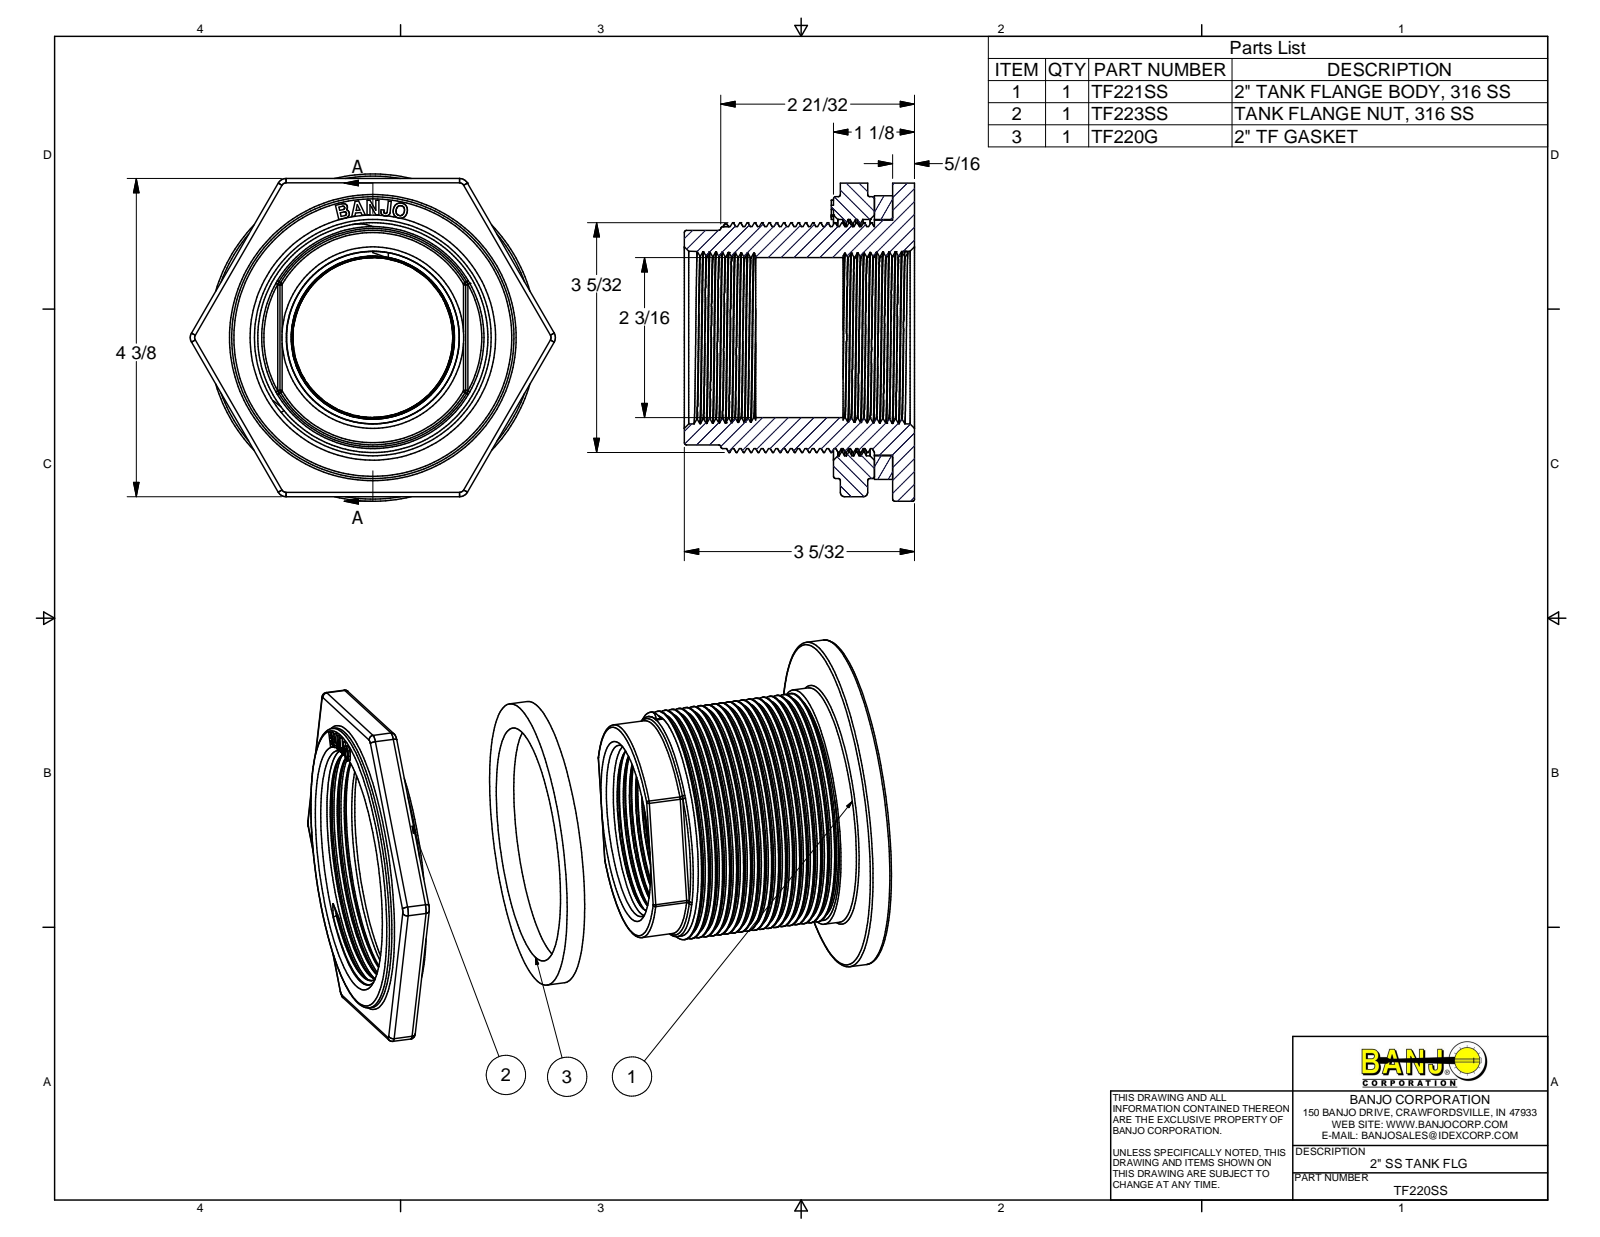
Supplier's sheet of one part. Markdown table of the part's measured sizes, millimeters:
| quantity | value |
| --- | --- |
| part name | TF220SS; TF221SS; TF223SS; TF220G |
| STEP written by | Autodesk Inventor 2013 (AUTOMOTIVE_DESIGN) |
| units | millimeters |
| bodies | 3 solids, 250 faces (78 planar, 64 cylindrical, 108 other) |
| overall size | 127.3 × 114.3 × 80.3 |
| volume | 294 800 mm³ |
| surface area | 91 810 mm² |
| round holes (diameter × count) | 55.9 × 1, 79.8 × 1, 82 × 1, 82.6 × 1 |
| round bosses / shafts (diameter × count) | 114.3 × 1, 99.1 × 1, 98.4 × 1, 80.3 × 1, 77.5 × 1 |
| partial cylindrical surfaces (radius × count) | 1.5 × 16, 3.2 × 6, 0.8 × 4, 12.7 × 1, 37.5 × 1 |
| main face-to-face distances | 7.6, 6.4, 14, 2.4, 11.9, 9.5, 18.3, 25.9, 8.7, 16.4 |
